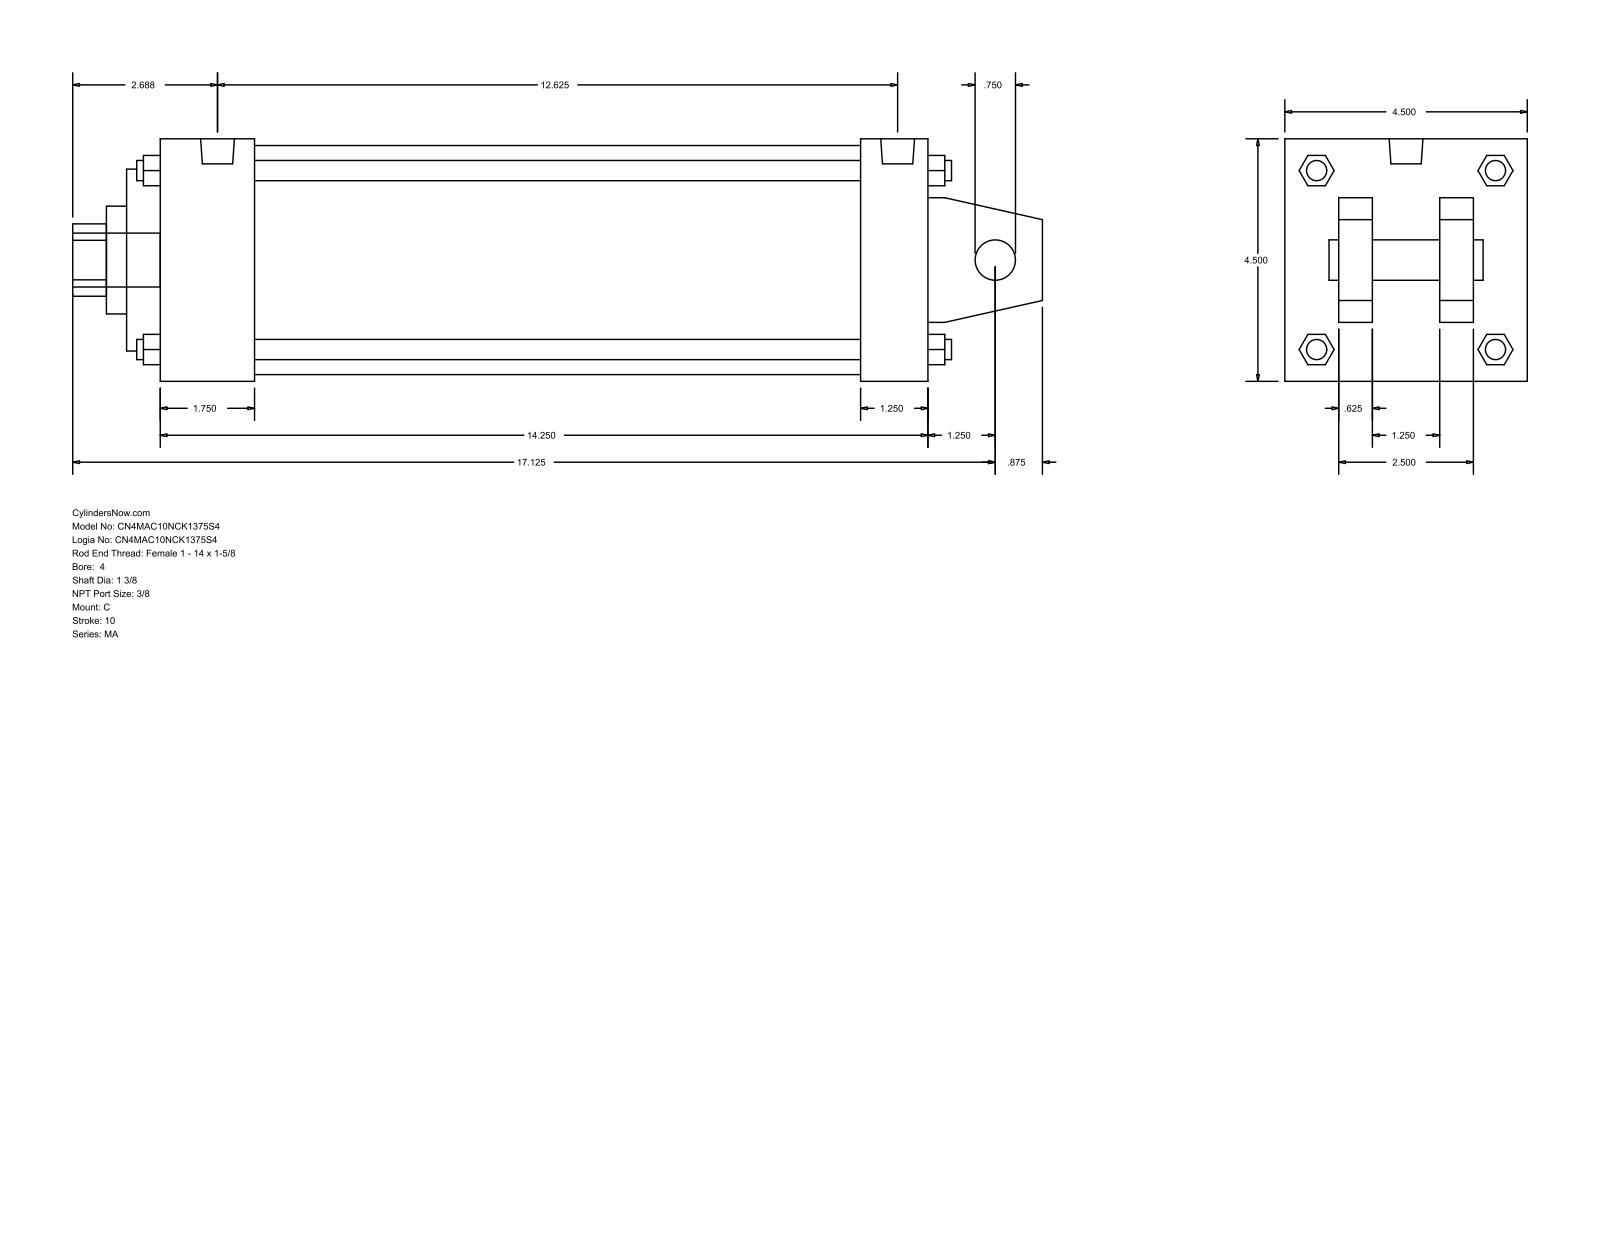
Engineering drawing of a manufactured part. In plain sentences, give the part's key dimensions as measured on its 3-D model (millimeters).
The part is named "MA_C__0400_1.375". Its 3-D file was written by "GSSL Pune (CONFIG_CONTROL_DESIGN)". It is 0 solids with 141 faces: 109 planar, 32 cylindrical and 0 other. Overall it measures 457.2 by 114.3 by 114.3 millimeters. Round holes: 1 of diameter 19.05, 1 of diameter 34.92, 1 of diameter 50.8, 1 of diameter 85.72, 1 of diameter 107.95. Round bosses or shafts: 4 of diameter 11.11, 4 of diameter 9.53, 2 of diameter 15.93, 1 of diameter 25.4. Partial cylindrical surfaces (rounded edges, fillets, slot ends): 1 of radius 17.06. The main face-to-face distances are 114.3, 15.87, 361.96, 73.03, 41.27, 25.4, 88.9, 47.63, 377.83, 346.08.
